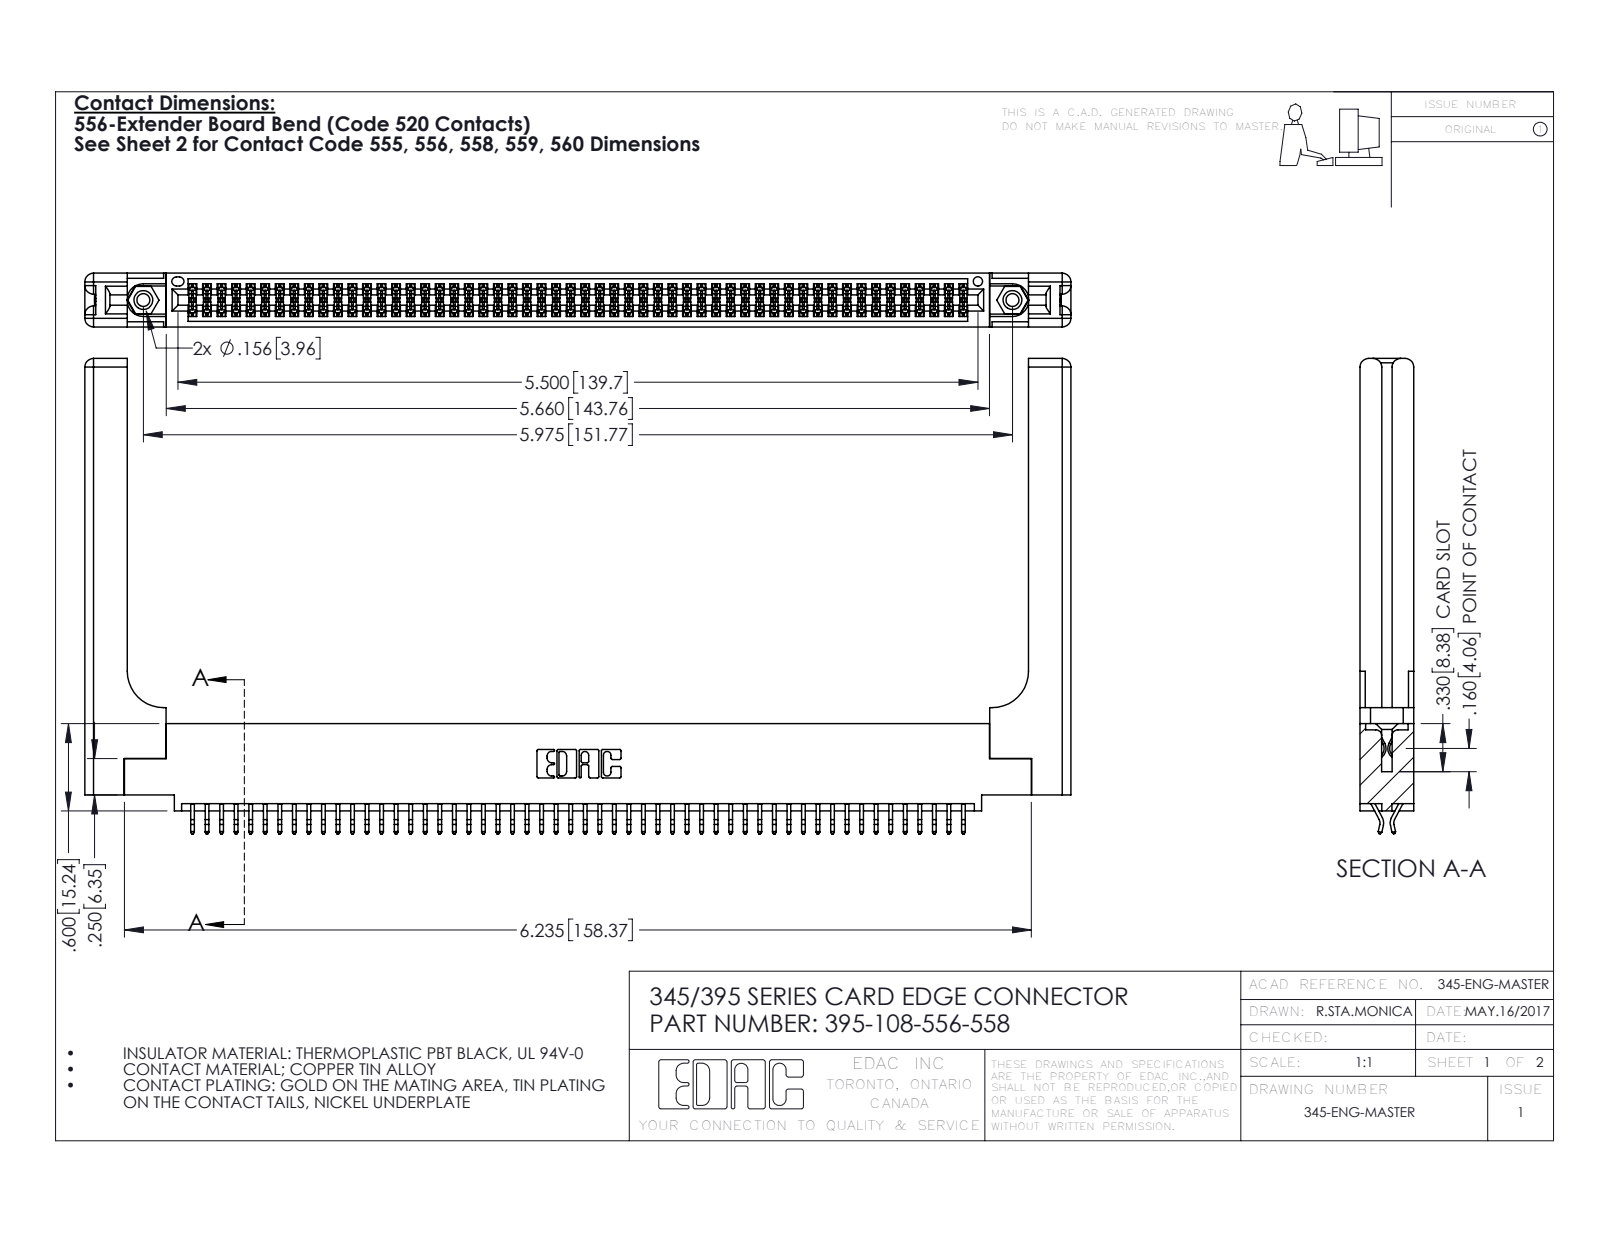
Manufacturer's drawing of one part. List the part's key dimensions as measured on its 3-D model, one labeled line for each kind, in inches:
Part name (STEP PRODUCT): 345 Part_0.110 Offset - 0.156 Dia-TH; 345-292-001_556 Tail; 345-250-001_345-250-001-102; 345-220-058_345-220-058 (+1 more)
STEP written by: SolidWorks 2016 (CONFIG_CONTROL_DESIGN)
Units: inches
Bodies: 113 solids, 6434 faces (4228 planar, 2146 cylindrical, 60 other)
Overall size (bounding box): 6.779 × 3.267 × 0.37
Volume: 1.54 in³ · Surface area: 46.6 in²
Round holes (diameter × count): ⌀0.089 ×2, ⌀0.125 ×2, ⌀0.156 ×2, ⌀0.064 ×1
Round bosses / shafts (diameter × count): ⌀0.155 ×2
Partial cylindrical surfaces — rounded edges, fillets, slot ends (radius × count): R0.006 ×162, R0.01 ×22, R0.06 ×16, R0.007 ×6, R0.031 ×6, R0.026 ×3, R0.01 ×2, R0.014 ×2
Main face-to-face distances: 0.072, 0.298, 0.37, 0.025, 0.098, 0.272, 0.2, 0.225, 0.148, 0.15
Hole centre spacings: 0.27, 5.739, 5.975
